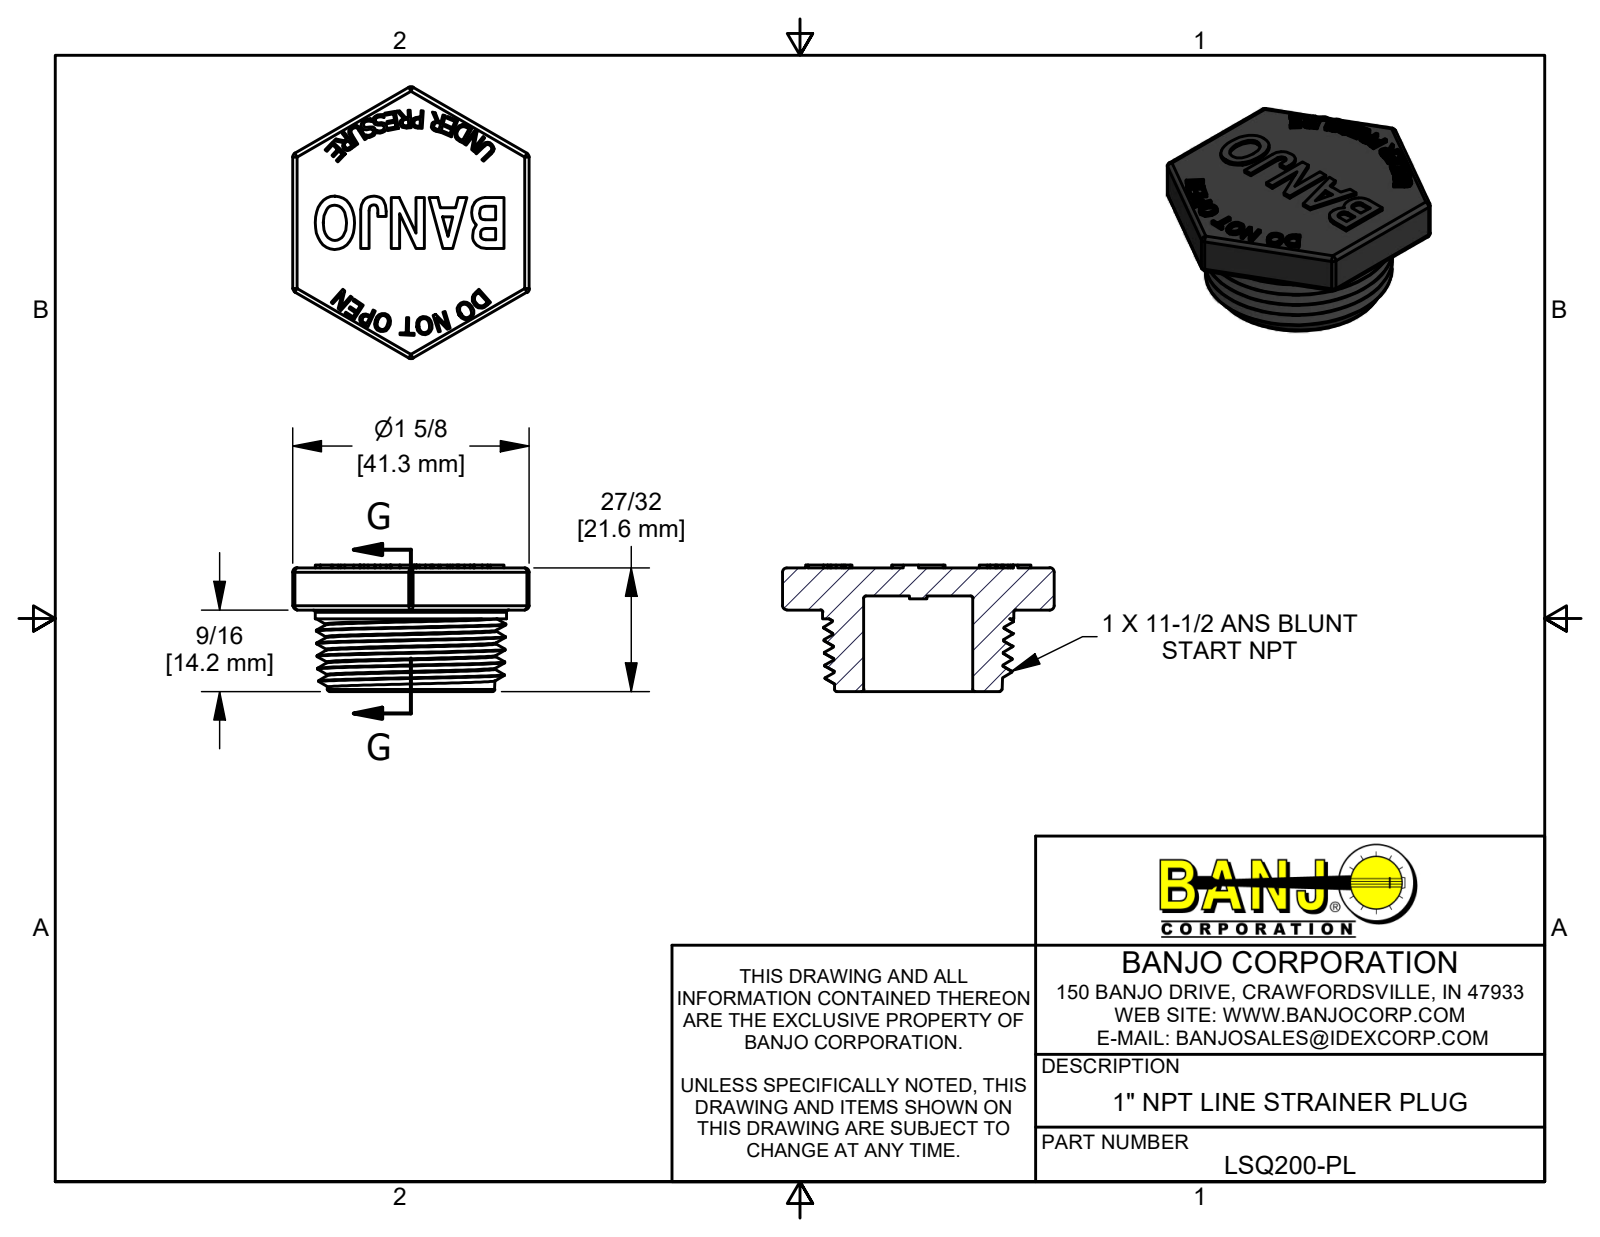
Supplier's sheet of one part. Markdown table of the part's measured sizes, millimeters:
| quantity | value |
| --- | --- |
| part name | LSQ200-PL |
| STEP written by | Autodesk Inventor 2017 (CONFIG_CONTROL_DESIGN) |
| units | millimeters |
| bodies | 0 solids, 491 faces (267 planar, 21 cylindrical, 203 other) |
| overall size | 47.42 × 41.27 × 22.1 |
| round holes (diameter × count) | 19.05 × 1 |
| round bosses / shafts (diameter × count) | 33.4 × 1 |
| partial cylindrical surfaces (radius × count) | 0.76 × 18, 0.13 × 1 |
| main face-to-face distances | 7.37, 41.28, 14.22, 21.59, 2.45, 16.67, 4.92, 0.51, 5.43, 22.1 |
